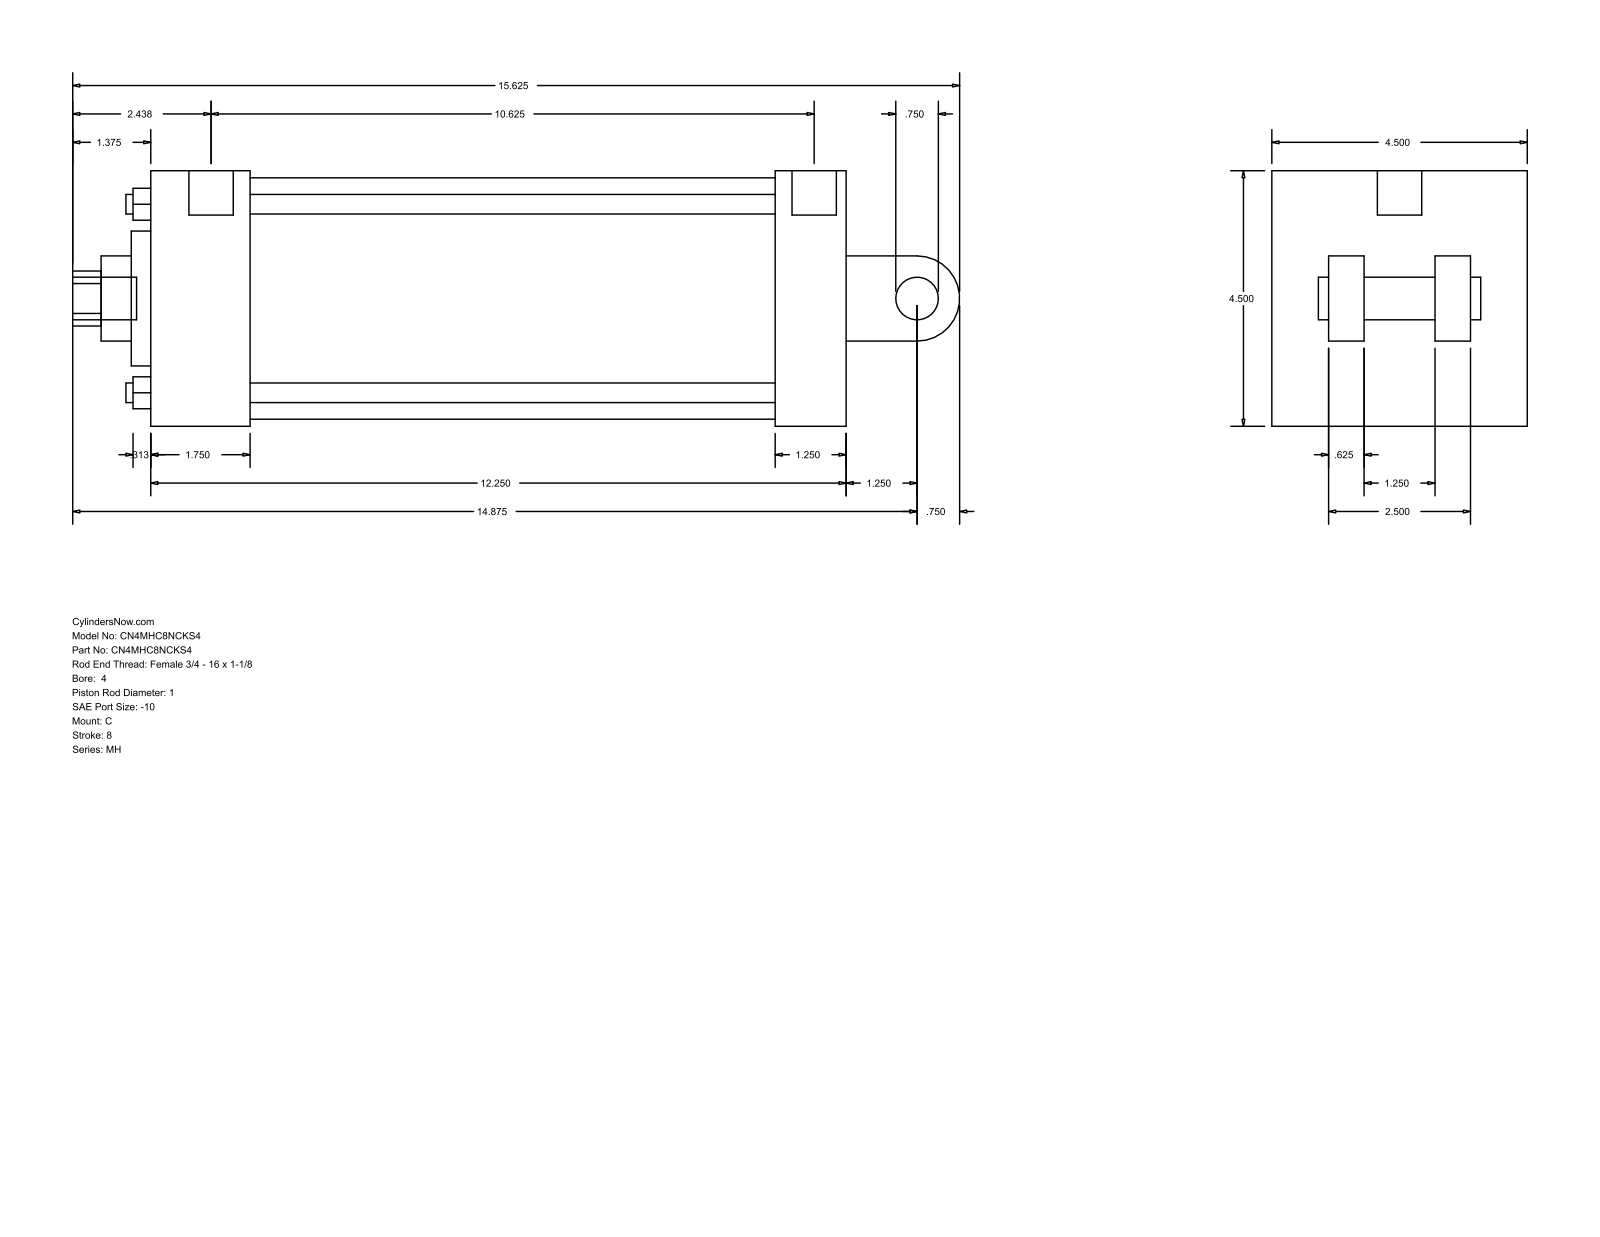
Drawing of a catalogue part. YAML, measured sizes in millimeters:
part_name: "MH_C__0400_1"
step_written_by: "GSSL Pune (CONFIG_CONTROL_DESIGN)"
units: millimeters
bodies: {solids: 0, faces: 101, planar: 71, cylindrical: 30, other: 0}
overall_size: [396.88, 114.3, 114.3]
round_holes:
  - {diameter: 8.76, count: 4}
  - {diameter: 8.73, count: 2}
  - {diameter: 19.84, count: 1}
  - {diameter: 25.4, count: 1}
  - {diameter: 38.1, count: 1}
  - {diameter: 60.33, count: 1}
  - {diameter: 107.95, count: 1}
round_bosses_or_shafts:
  - {diameter: 19.05, count: 2}
  - {diameter: 8.73, count: 2}
  - {diameter: 19.84, count: 1}
partial_cylinders:
  - {radius: 12.29, count: 1}
  - {radius: 19.05, count: 1}
face_to_face_distances: [114.3, 311.15, 44.46, 279.4, 234.94, 266.69, 31.75, 73.03, 15.87, 47.63]
hole_center_spacings: [59.62, 84.32, 119.25, 1.59]
